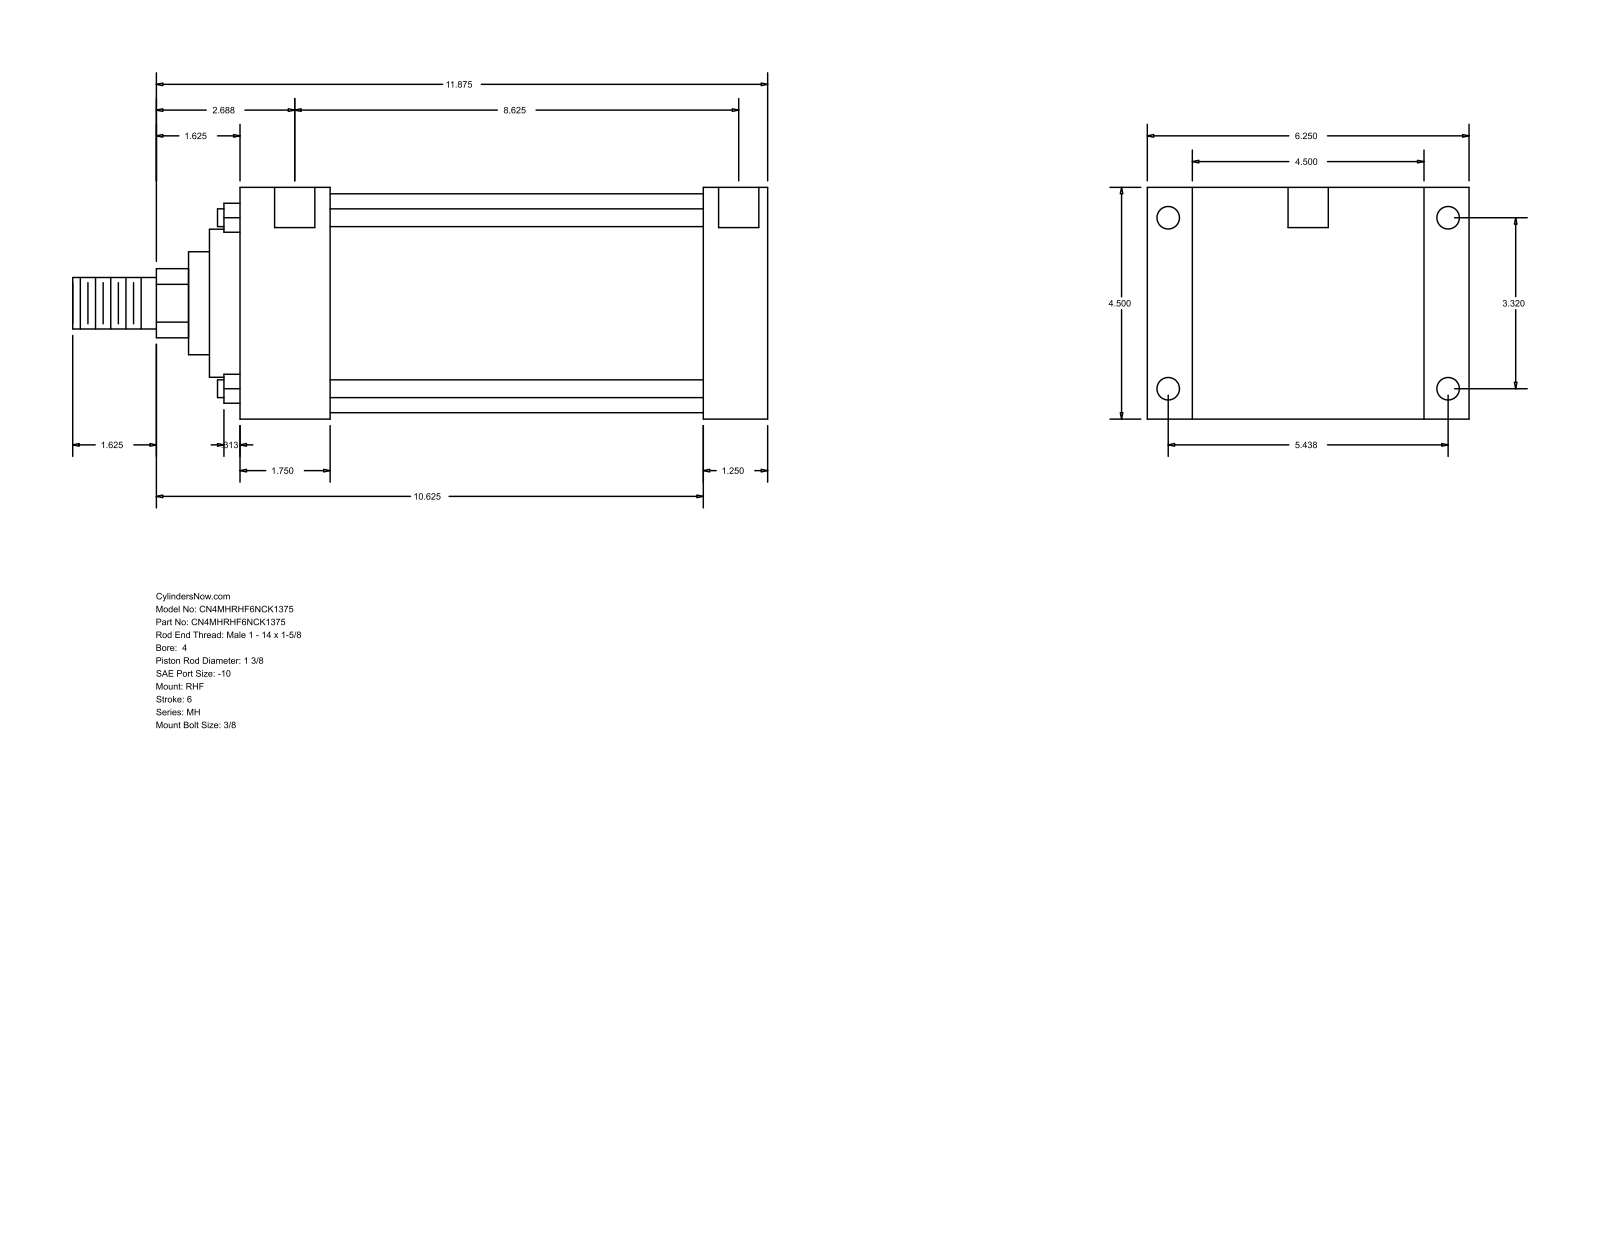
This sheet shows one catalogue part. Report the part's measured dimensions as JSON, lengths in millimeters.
{"part_name": "MH_RHF__0400_1.375", "step_written_by": "GSSL Pune (CONFIG_CONTROL_DESIGN)", "units": "millimeters", "bodies": {"solids": 0, "faces": 90, "planar": 61, "cylindrical": 29, "other": 0}, "overall_size": [342.9, 158.75, 114.3], "round_holes": [[8.73, 4], [11.13, 4], [19.84, 2]], "round_bosses_or_shafts": [[8.76, 4], [107.95, 1], [73.03, 1], [50.8, 1], [34.92, 1], [25.4, 1]], "partial_cylinders_radius": [[17.06, 1]], "face_to_face_distances": [114.3, 31.74, 228.61, 260.35, 22.23, 136.53, 44.45, 184.16, 215.9, 158.76], "hole_center_spacings": [1.59, 84.32, 138.12, 161.82, 220.67, 222.26, 219.08]}
